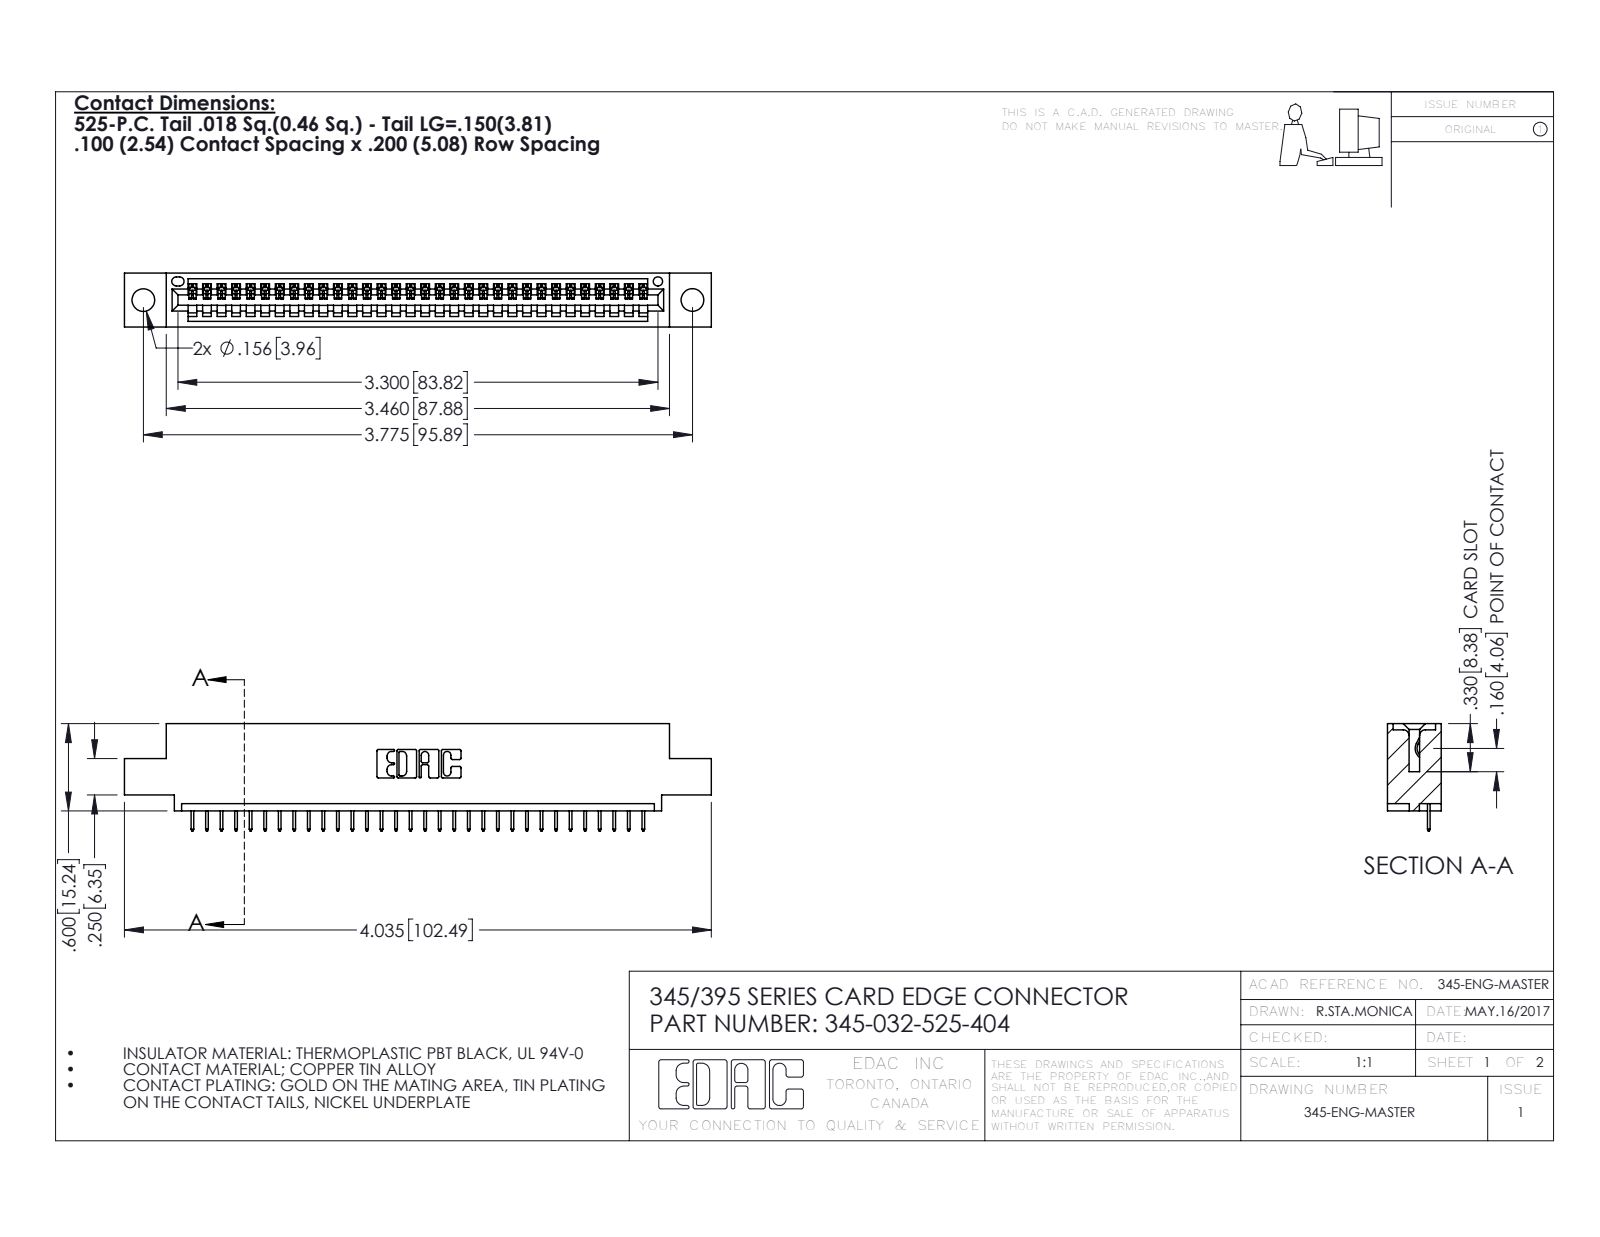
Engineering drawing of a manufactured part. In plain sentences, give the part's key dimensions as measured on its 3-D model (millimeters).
The part is named "345 Part_0.110 Offset - 0.156 Dia-TH; 345-032-525-404; 345-292-001_345-293-125". Its 3-D file was written by "SolidWorks 2020 (CONFIG_CONTROL_DESIGN)". It is 33 solids with 2114 faces: 1556 planar, 558 cylindrical and 0 other. Overall it measures 102.5 by 18.7 by 9.4 millimeters. Its volume is 9 360 cubic millimeters and its surface area 11 760 square millimeters. Round holes: 2 of diameter 4, 1 of diameter 1.6. Partial cylindrical surfaces (rounded edges, fillets, slot ends): 64 of radius 0.2, 22 of radius 0.3, 6 of radius 0.2, 6 of radius 0.8, 3 of radius 0.7, 2 of radius 0.8, 2 of radius 1, 1 of radius 0.4. The main face-to-face distances are 1.8, 7.6, 9.4, 5.1, 2.5, 6.9, 0.6, 5.7, 1.8, 3.8. The hole center spacings are 6.9, 89.9, 95.9.
